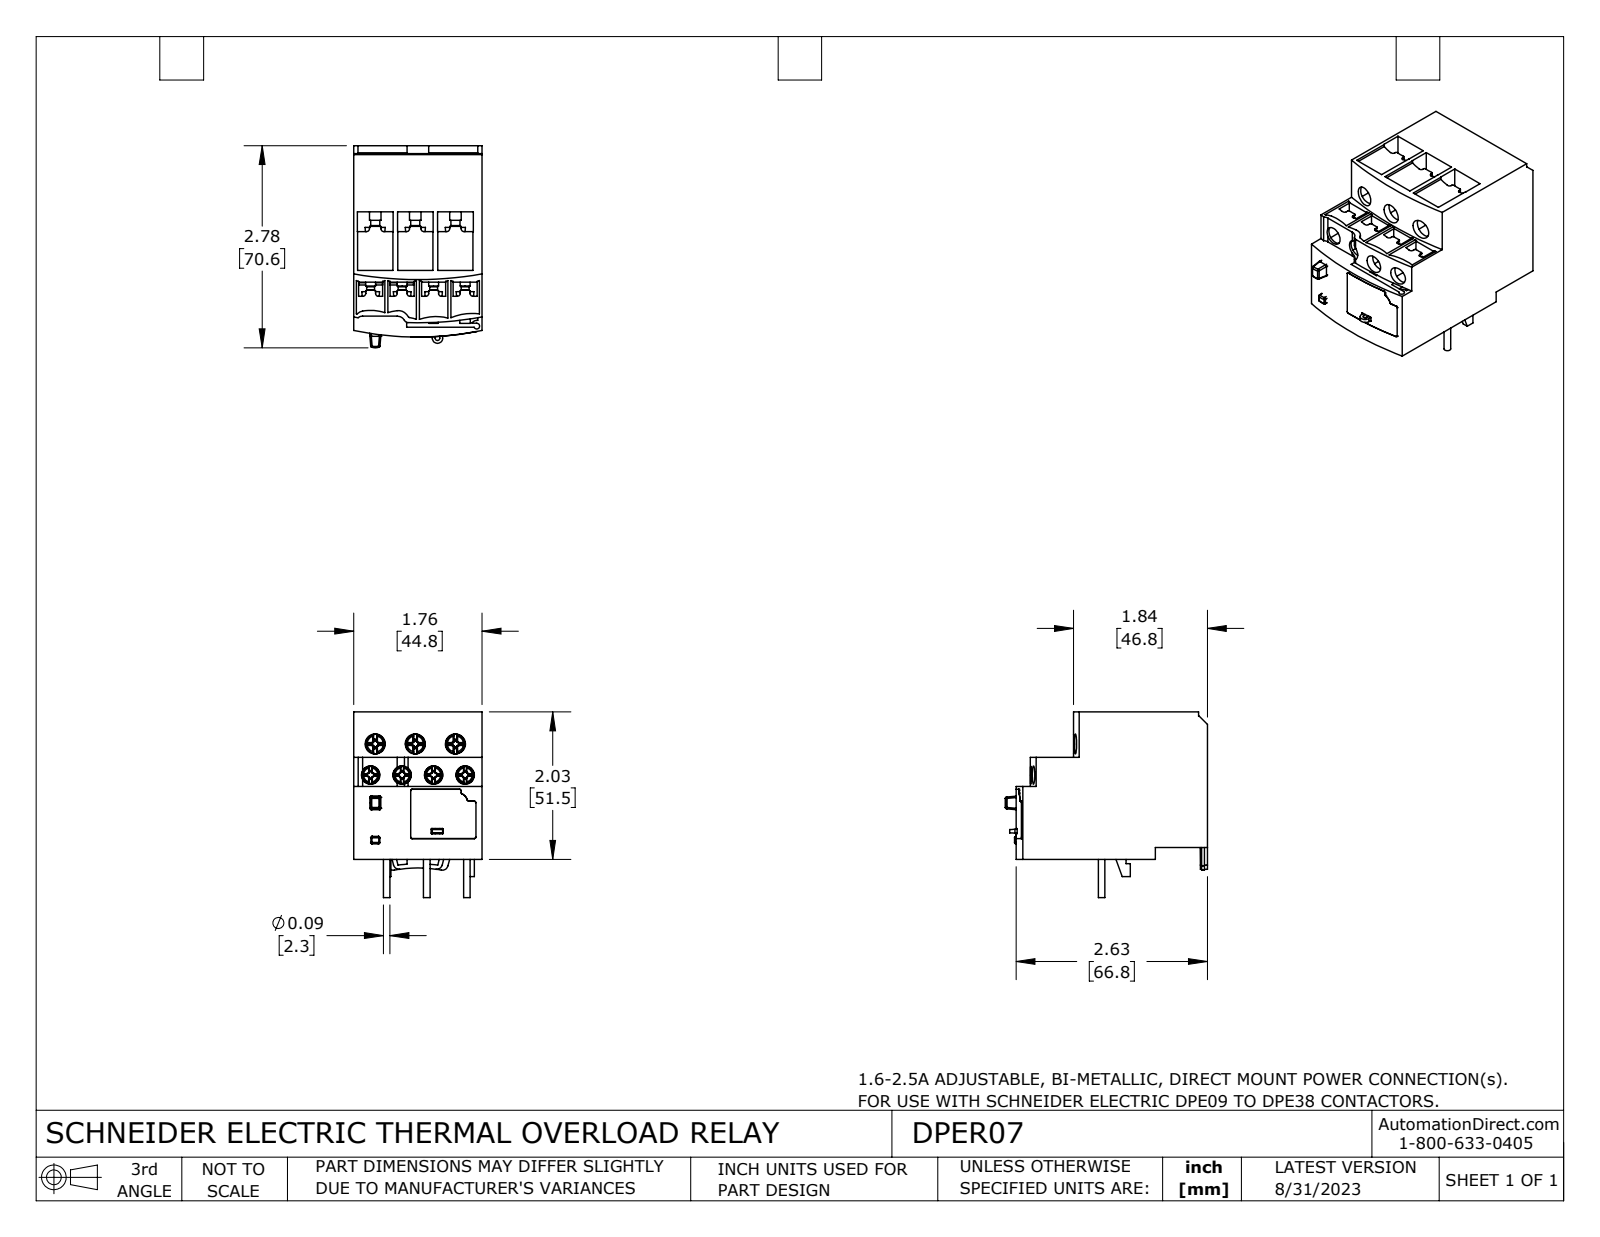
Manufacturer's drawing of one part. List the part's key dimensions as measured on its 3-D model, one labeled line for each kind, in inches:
Part name (STEP PRODUCT): DPER07
STEP written by: SolidWorks 2021 (CONFIG_CONTROL_DESIGN)
Units: inches
Bodies: 16 solids, 1212 faces (676 planar, 269 cylindrical, 267 other)
Overall size (bounding box): 2.778 × 2.553 × 1.764
Volume: 6.953 in³ · Surface area: 47.15 in²
Round holes (diameter × count): ⌀0.252 ×4, ⌀0.276 ×3, ⌀0.079 ×2, ⌀0.118 ×2, ⌀0.059 ×1, ⌀0.244 ×1
Round bosses / shafts (diameter × count): ⌀0.091 ×12, ⌀0.138 ×4, ⌀0.108 ×4, ⌀0.157 ×3, ⌀0.154 ×3, ⌀0.124 ×3, ⌀0.118 ×1, ⌀0.107 ×1
Partial cylindrical surfaces — rounded edges, fillets, slot ends (radius × count): R0.02 ×52, R0.039 ×22, R0.004 ×19, R0.012 ×8, R0.008 ×6, R0.63 ×6, R0.079 ×4, R0.024 ×2
Main face-to-face distances: 1.764, 0.165, 2.028, 1.863, 0.909, 0.551, 0.618, 1.409, 1.245, 2.497
Hole centre spacings: 0.433, 0.551, 0.866, 0.334, 0.381, 0.404, 0.422, 0.449
